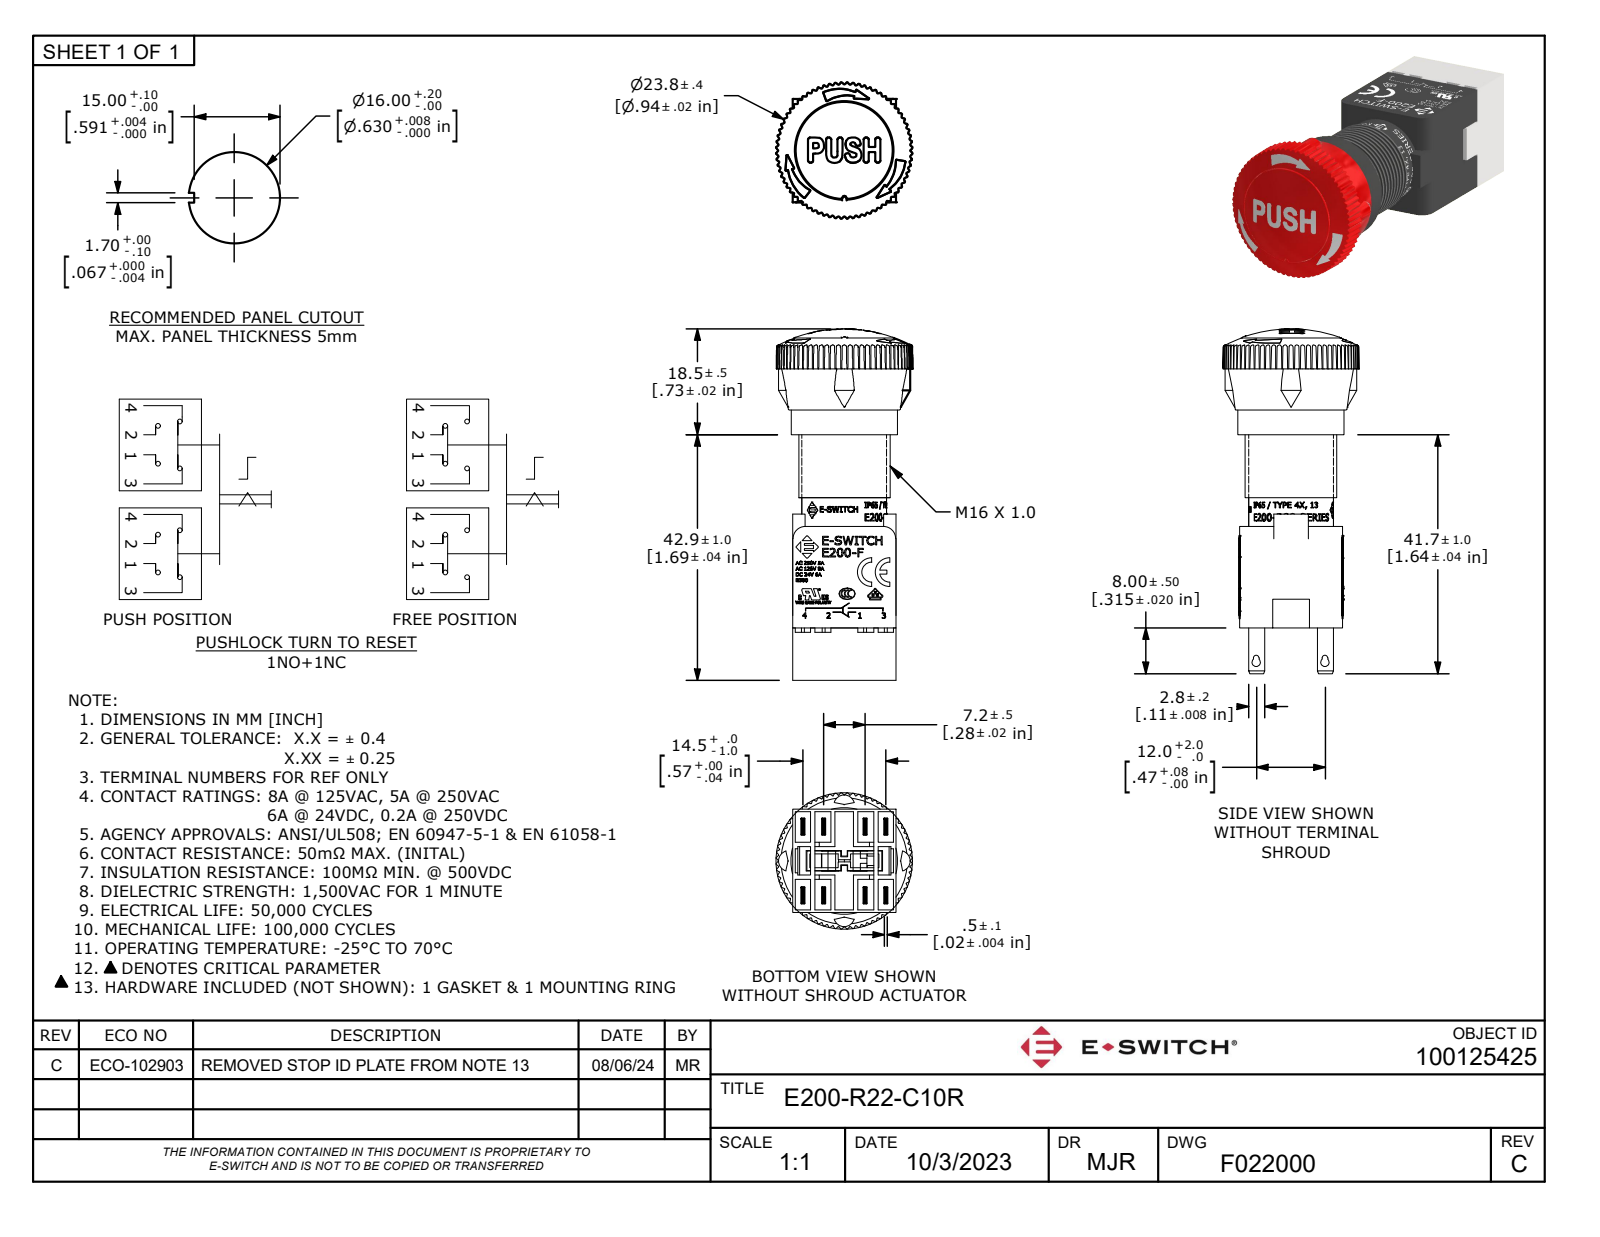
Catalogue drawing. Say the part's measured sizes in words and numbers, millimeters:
The part is named "E200-R22-C10R". Its 3-D file was written by "Autodesk Inventor 2022 (AUTOMOTIVE_DESIGN)". It is 1 solid with 4241 faces: 2734 planar, 255 cylindrical and 1252 other. Overall it measures 61.4 by 23.78 by 23.78 millimeters. Its volume is 15 418 cubic millimeters and its surface area 9 838 square millimeters. Round holes: 2 of diameter 0.33, 1 of diameter 17.2, 1 of diameter 18.5. Round bosses or shafts: 2 of diameter 0.37, 1 of diameter 18.55, 1 of diameter 17, 1 of diameter 16, 1 of diameter 14.8. Partial cylindrical surfaces (rounded edges, fillets, slot ends): 72 of radius 0.1, 16 of radius 0.1, 6 of radius 0.57, 6 of radius 0.66, 4 of radius 0.14, 4 of radius 0.18, 4 of radius 0.26, 4 of radius 1.72. The main face-to-face distances are 18, 0.5, 0.45, 17.55, 6.75, 3.5, 7.2, 10.35, 10.25, 14.47. The hole center spacings are 8.72.
